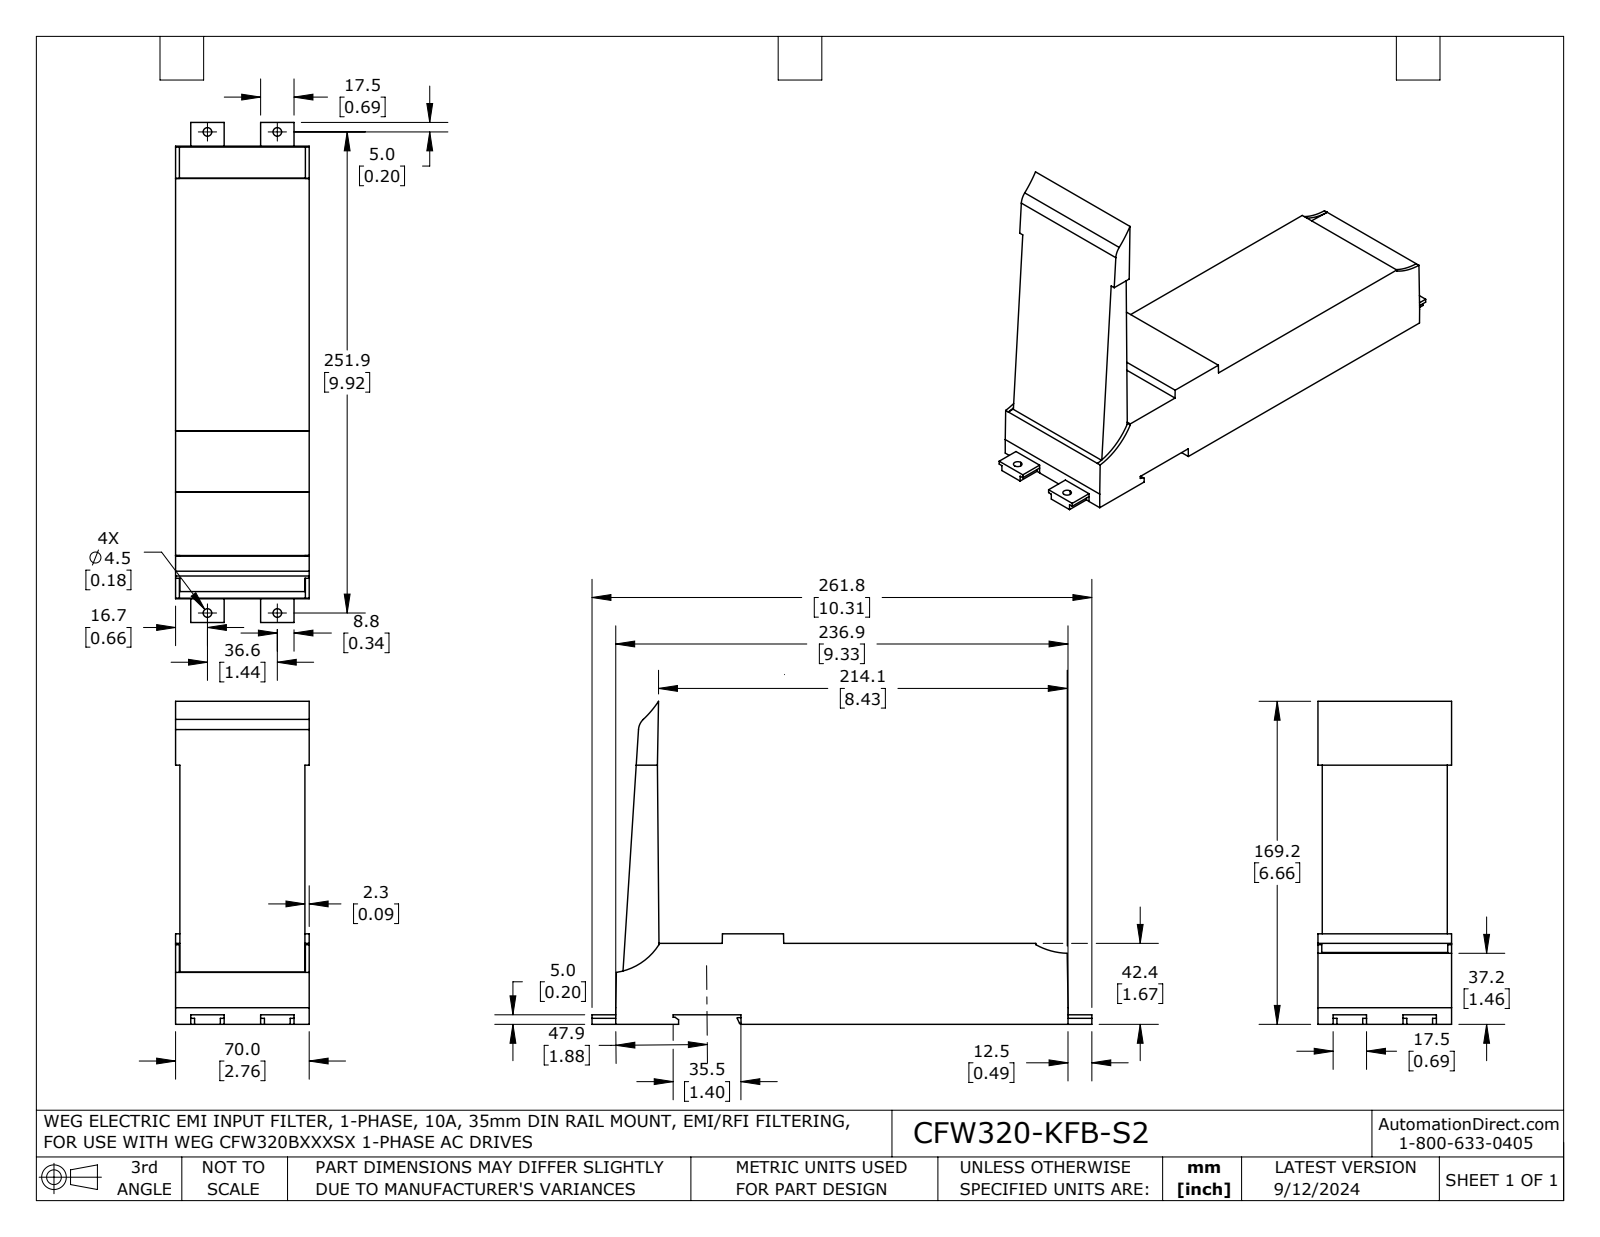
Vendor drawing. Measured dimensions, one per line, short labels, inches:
name: CFW320-KFB-S2
written by: SolidWorks 2021 (AUTOMOTIVE_DESIGN)
unit: in
bodies: 1 solid, 110 faces (95 planar, 15 cylindrical, 0 other)
size: 10.309 × 6.66 × 2.756
volume: 48.97 in³; area: 127.7 in²
holes: 4× ⌀0.177
rounds: 1× R0.039, 1× R0.315, 1× R1.26, 1× R1.401, 1× R2.081
face distances: 1.669, 2.756, 0.197, 1.472, 0.089, 2.667, 1.866, 2.579, 0.775, 0.079
hole spacings: 1.441, 9.917, 10.022
